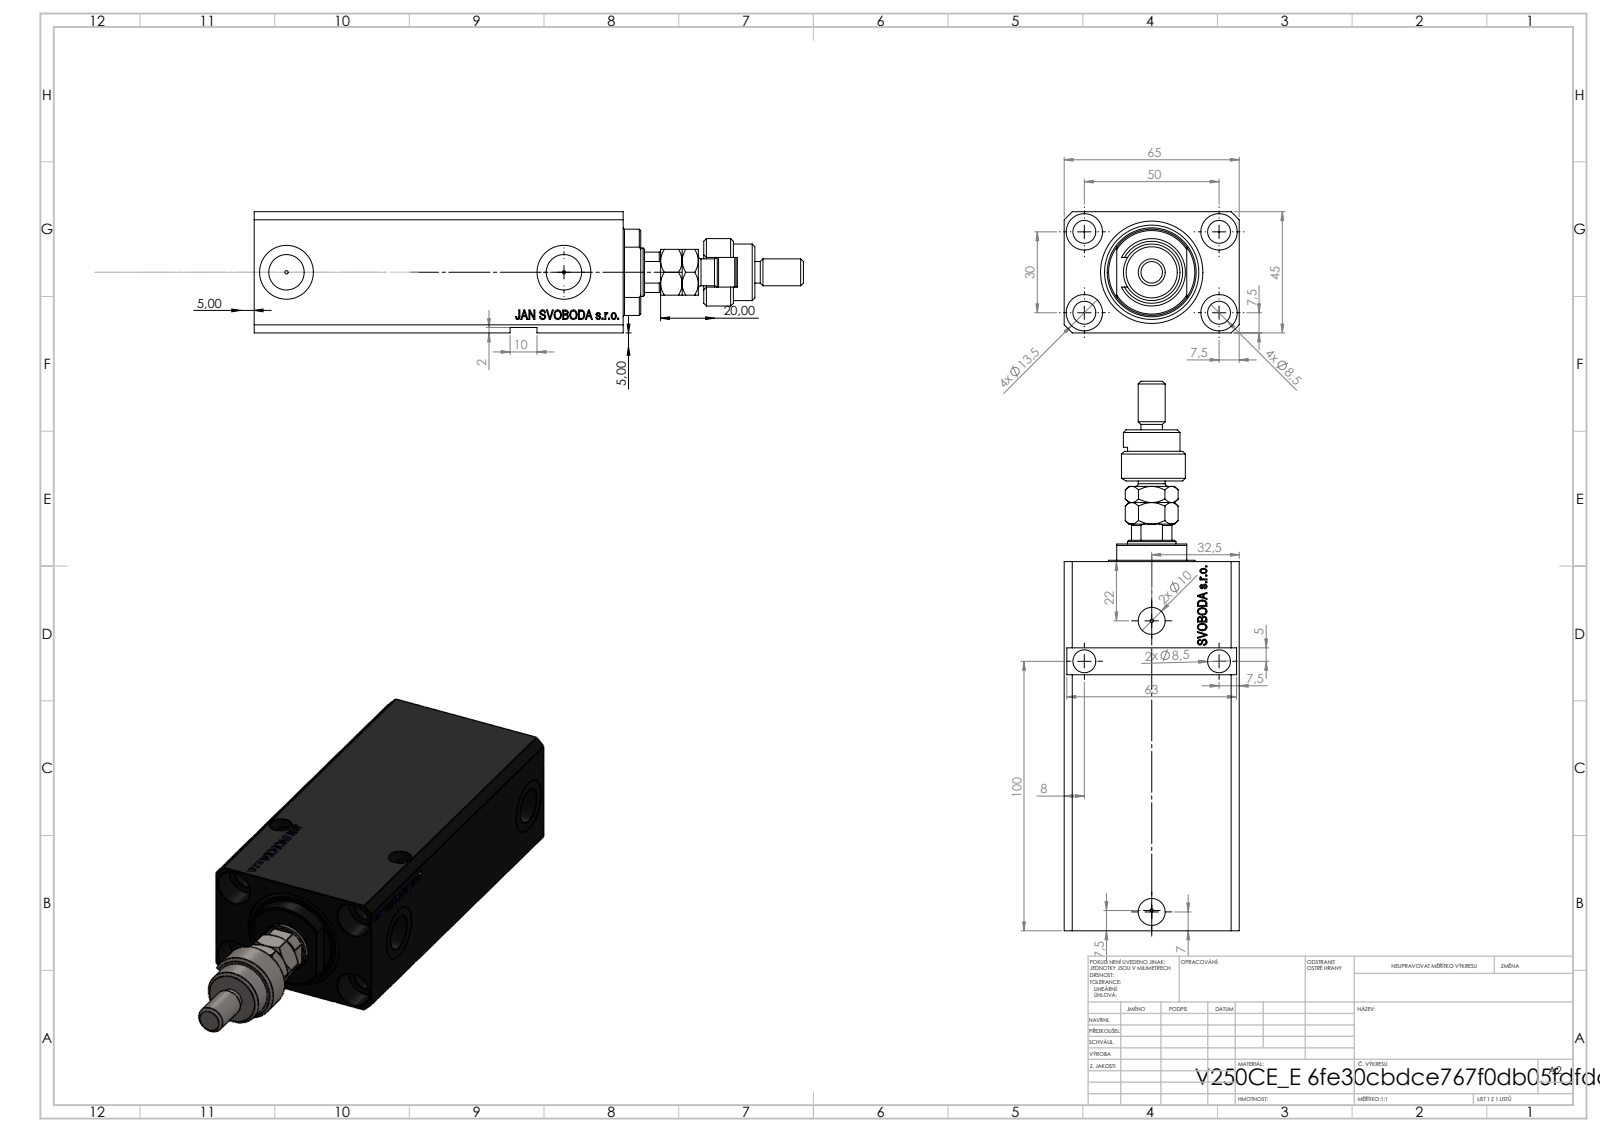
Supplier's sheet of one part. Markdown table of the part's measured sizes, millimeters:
| quantity | value |
| --- | --- |
| part name | V250CE_E_Body; MFA; FEMALE_PART_FOR_DFA; V250CE_VC_E (+1 more) |
| STEP written by | SolidWorks 2019 (CONFIG_CONTROL_DESIGN) |
| units | millimeters |
| bodies | 5 solids, 1018 faces (467 planar, 129 cylindrical, 422 other) |
| overall size | 204 × 65 × 45 |
| volume | 343 040 mm³ |
| surface area | 87 154 mm² |
| round holes (diameter × count) | 8.5 × 9, 1.25 × 4, 13.5 × 4, 10 × 2, 13.16 × 2, 20 × 2, 18 × 1, 38 × 1 |
| round bosses / shafts (diameter × count) | 25 × 1, 21 × 1, 16 × 1, 10 × 1, 8 × 1 |
| partial cylindrical surfaces (radius × count) | 5.5 × 1, 8.5 × 1, 8.75 × 1, 16 × 1 |
| main face-to-face distances | 45, 65, 14, 123, 137, 6.9, 116.1, 130.1, 28, 43 |
| hole center spacings | 29.15, 50, 30, 33.61, 33.97, 58.31, 70, 86.02 |
